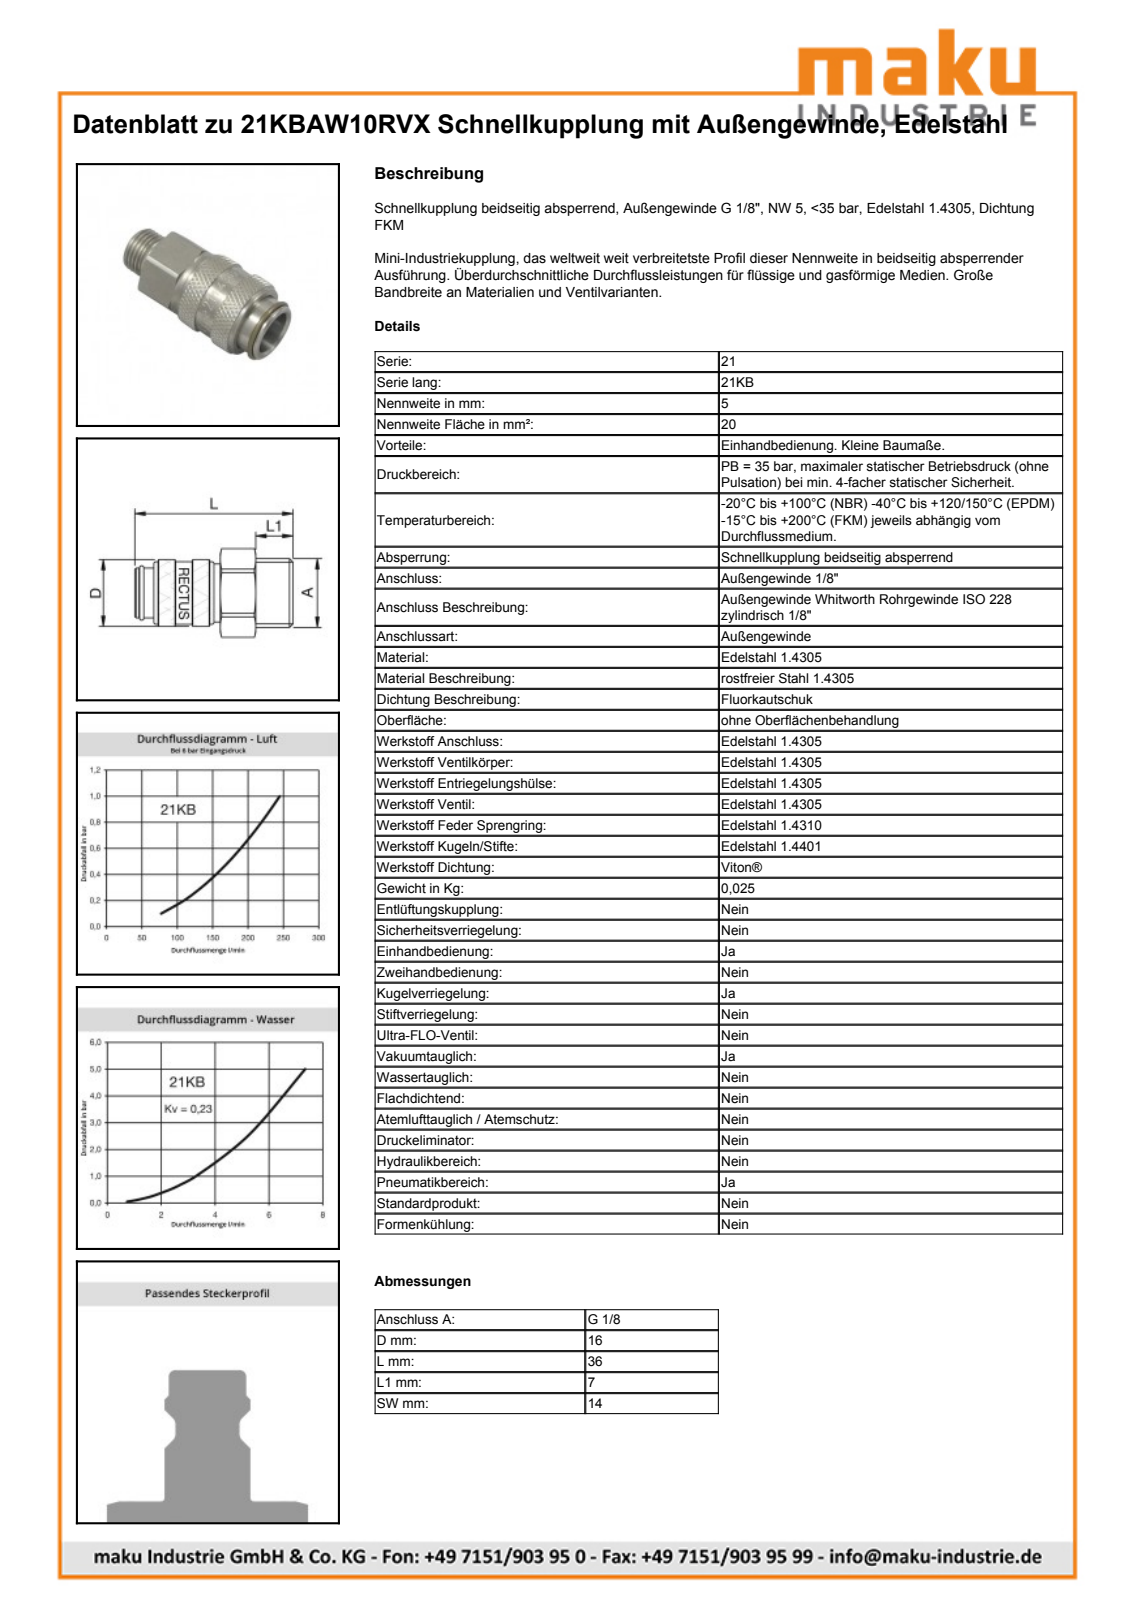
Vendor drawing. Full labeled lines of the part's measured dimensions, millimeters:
Part name (STEP PRODUCT): D106972
STEP written by: Autodesk Inventor 2013 (AUTOMOTIVE_DESIGN)
Units: millimetres
Bodies: 2 solids, 398 faces (130 planar, 61 cylindrical, 207 other)
Overall size (bounding box): 36.15 × 16.15 × 16.15
Volume: 5 172 mm³ · Surface area: 3 377 mm²
Round holes (diameter × count): ⌀12.15 ×1, ⌀14 ×1
Round bosses / shafts (diameter × count): ⌀16.15 ×1, ⌀15.1 ×1, ⌀12 ×1, ⌀11.4 ×1, ⌀11.15 ×1, ⌀9.86 ×1, ⌀9.73 ×1
Partial cylindrical surfaces — rounded edges, fillets, slot ends (radius × count): R5.64 ×1, R7.45 ×1, R7.9 ×1
Main face-to-face distances: 14, 29.15, 36.15, 7, 11.55, 16.15, 13, 20, 4.6, 24.55
